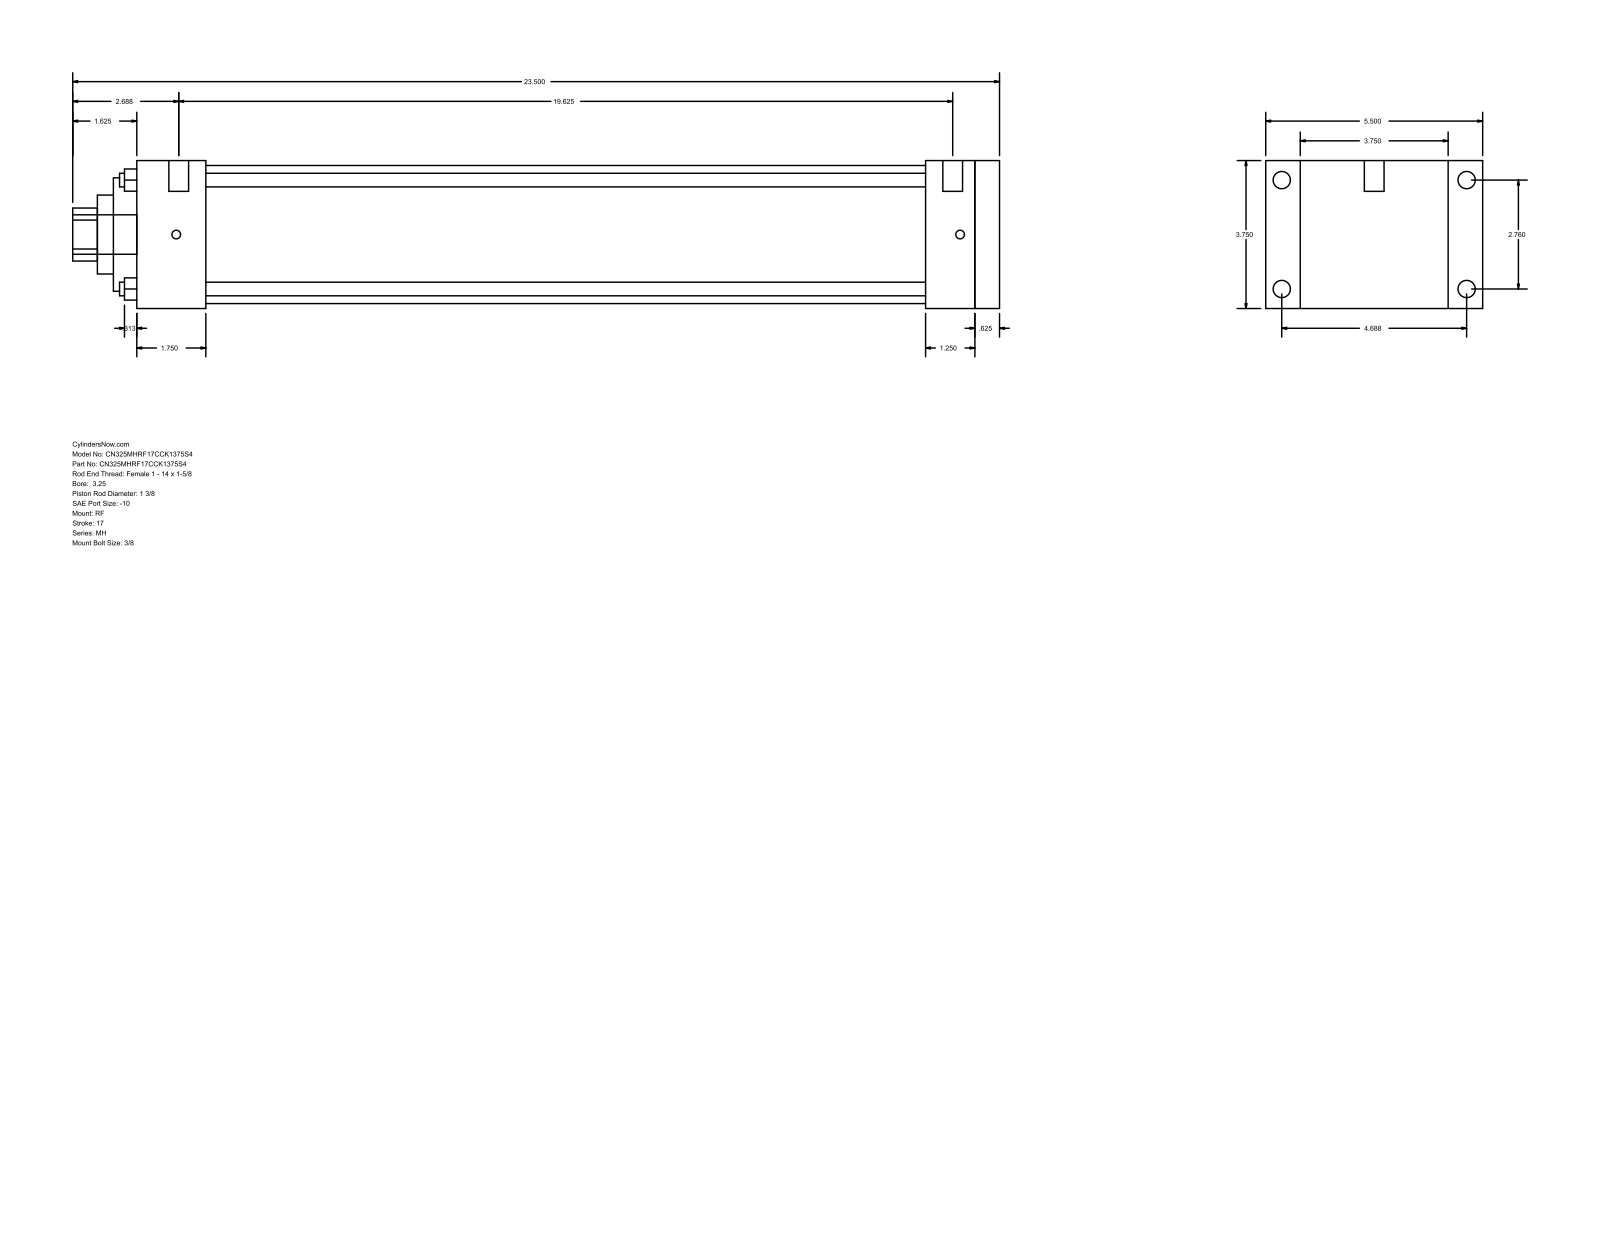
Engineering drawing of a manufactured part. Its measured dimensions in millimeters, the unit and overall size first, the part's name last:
Units: millimetres
Overall size (bounding box): 596.9 × 139.7 × 95.25
Round holes (diameter × count): ⌀8.76 ×4, ⌀34.92 ×1, ⌀50.8 ×1, ⌀73.03 ×1, ⌀88.9 ×1
Round bosses / shafts (diameter × count): ⌀11.13 ×4, ⌀5.56 ×4, ⌀12.7 ×2, ⌀25.4 ×1
Partial cylindrical surfaces — rounded edges, fillets, slot ends (radius × count): R17.06 ×1
Main face-to-face distances: 95.24, 555.63, 15.88, 539.75, 22.23, 117.47, 44.45, 495.3, 511.18, 508
Hole centre spacings: 49.57, 70.1, 99.14
Bodies: 0 solids, 94 faces (65 planar, 29 cylindrical, 0 other)
Part name (STEP PRODUCT): MH_RF__0325_1.375
STEP written by: GSSL Pune (CONFIG_CONTROL_DESIGN)
